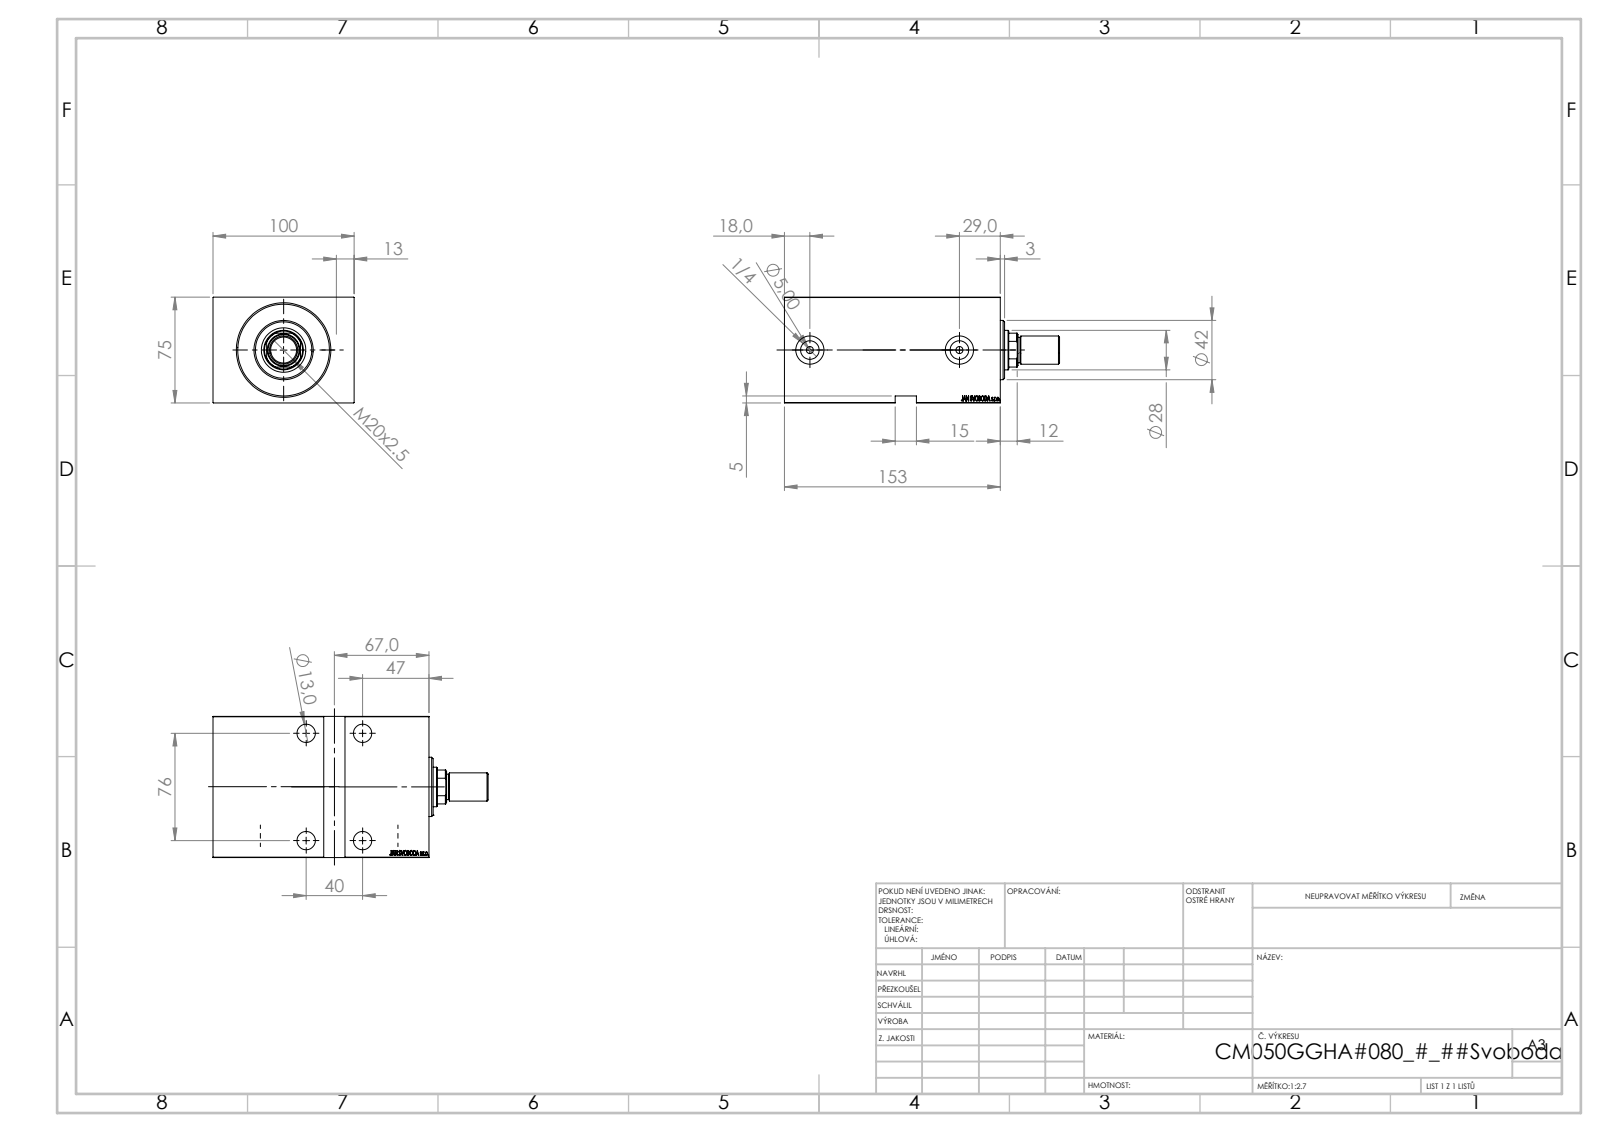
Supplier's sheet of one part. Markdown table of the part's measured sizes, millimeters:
| quantity | value |
| --- | --- |
| part name | V450CM_VC_G; V450CM_G_VCP; Zatka_OIL_PORT; V450CM_MALE_METRIC (+1 more) |
| STEP written by | SolidWorks 2019 (CONFIG_CONTROL_DESIGN) |
| units | millimeters |
| bodies | 6 solids, 908 faces (444 planar, 60 cylindrical, 404 other) |
| overall size | 195 × 100 × 75 |
| volume | 977 713 mm³ |
| surface area | 139 441 mm² |
| round holes (diameter × count) | 13 × 4, 19 × 4, 5 × 2, 13.16 × 2, 20 × 2, 18.5 × 1, 28 × 1, 31.5 × 1, 50 × 1, 52 × 1, 65 × 1 |
| round bosses / shafts (diameter × count) | 18 × 3, 42 × 1, 20 × 1 |
| partial cylindrical surfaces (radius × count) | 13.5 × 1 |
| main face-to-face distances | 75, 100, 153, 5, 134, 14, 139, 148, 47, 70 |
| hole center spacings | 40, 76, 85.88, 106 |
